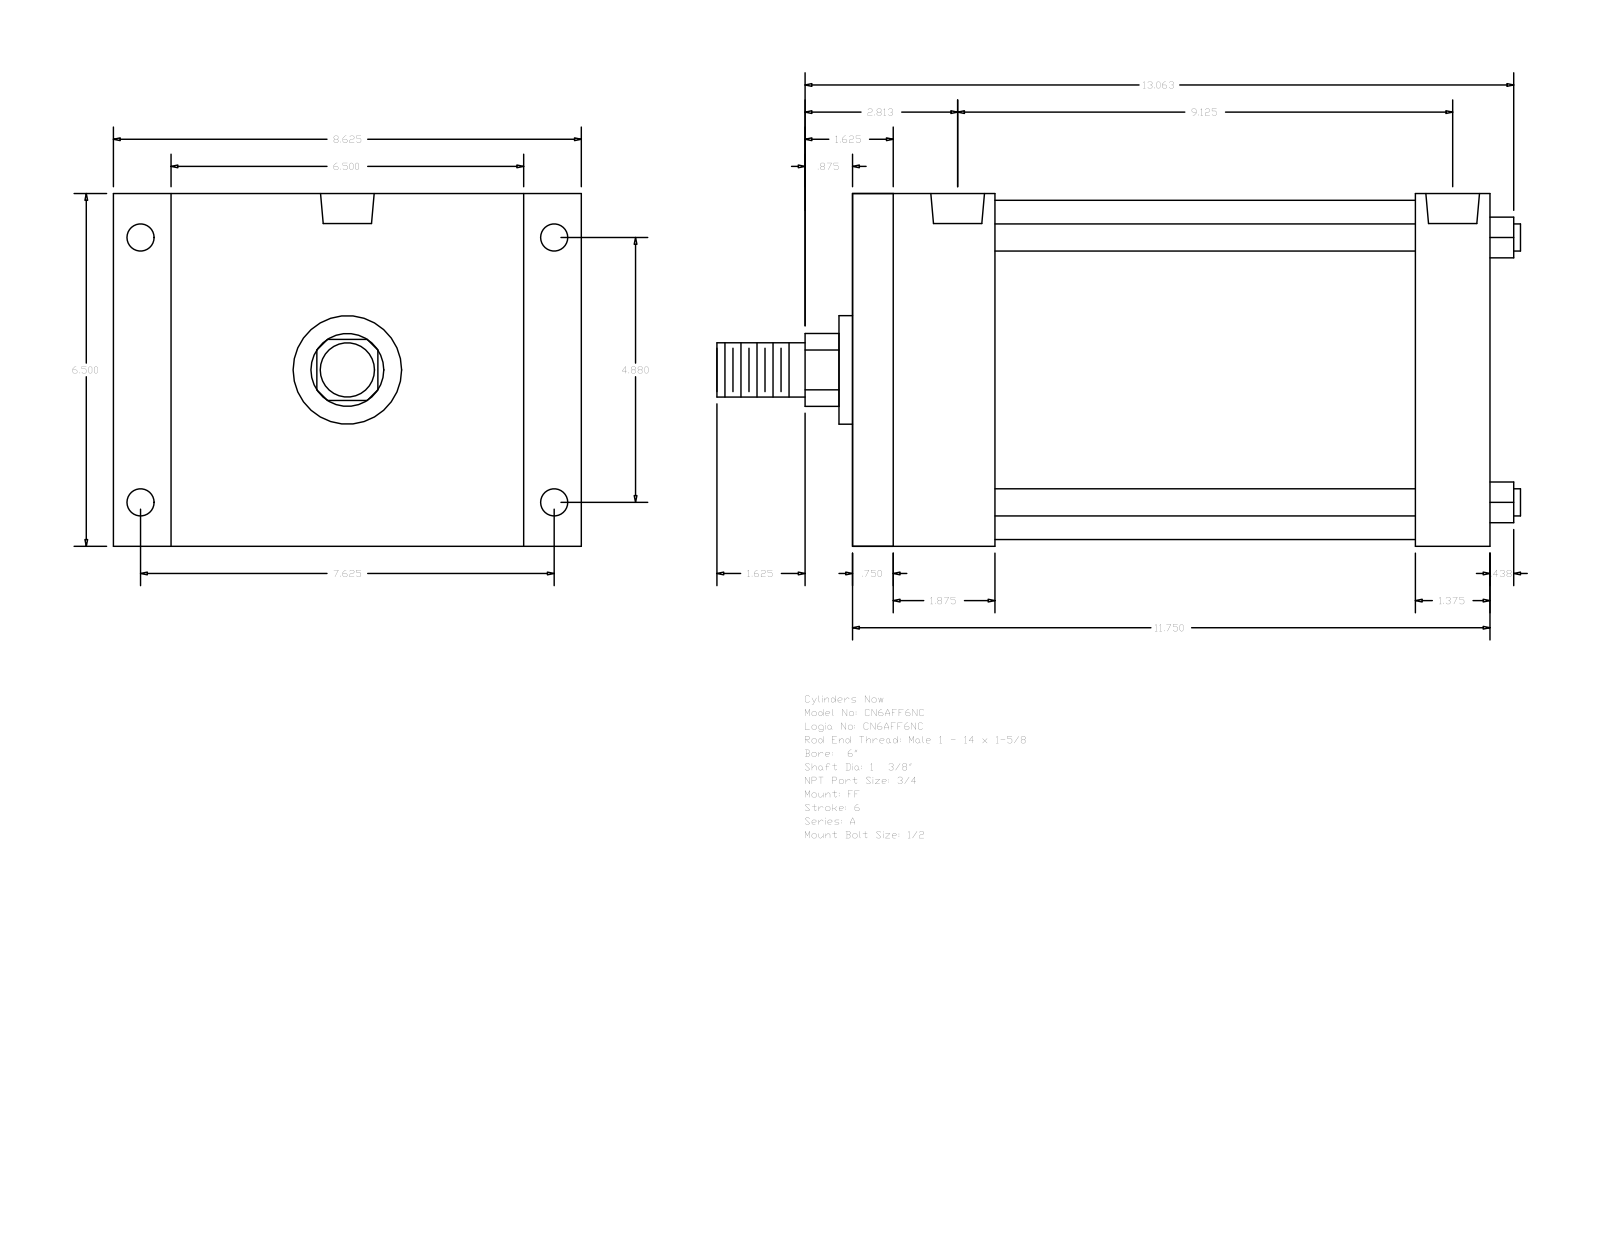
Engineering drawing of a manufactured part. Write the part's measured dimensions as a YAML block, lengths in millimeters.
part_name: "A_FF__0600_1.375"
step_written_by: "GSSL Pune (CONFIG_CONTROL_DESIGN)"
units: millimeters
bodies: {solids: 0, faces: 92, planar: 64, cylindrical: 28, other: 0}
overall_size: [376.24, 219.07, 165.1]
round_holes:
  - {diameter: 12.7, count: 4}
  - {diameter: 15.08, count: 4}
  - {diameter: 25.12, count: 2}
round_bosses_or_shafts:
  - {diameter: 12.7, count: 4}
  - {diameter: 158.75, count: 1}
  - {diameter: 50.8, count: 1}
  - {diameter: 34.92, count: 1}
  - {diameter: 25.4, count: 1}
partial_cylinders:
  - {radius: 17.06, count: 1}
face_to_face_distances: [165.1, 298.45, 19.04, 279.41, 66.67, 47.63, 231.78, 263.52, 244.48, 196.85]
hole_center_spacings: [5.56, 123.96, 193.68, 220.65, 226.21, 229.95, 231.77]
